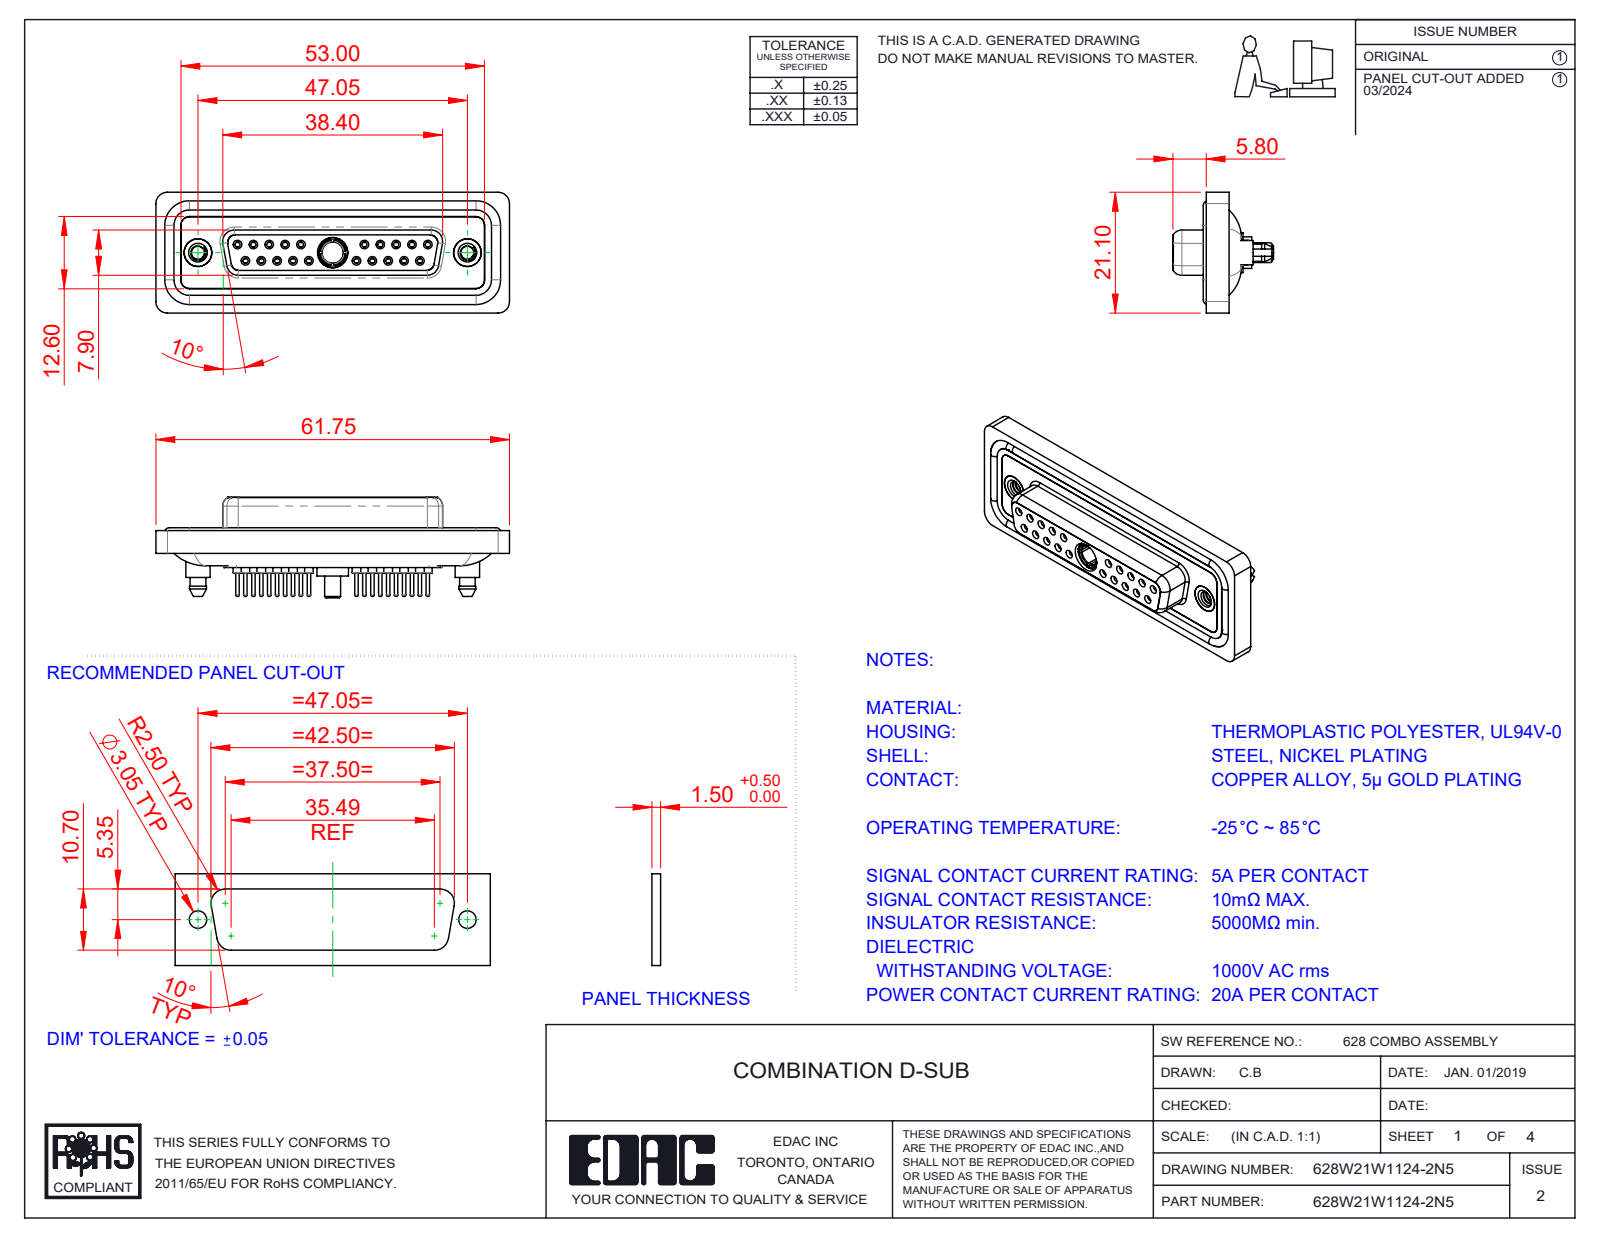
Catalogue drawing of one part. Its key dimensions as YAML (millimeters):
part_name: "628Combo Shell Front_25 Contacts; 628Combo Waterproof Housing_25 Contacts; 628Combo Contact Row 2_24; 628Combo Housing_21W1 (+5 more)"
step_written_by: "SolidWorks 2023 (CONFIG_CONTROL_DESIGN)"
units: millimeters
bodies: {solids: 29, faces: 1610, planar: 450, cylindrical: 623, other: 537}
overall_size: [61.75, 21.1, 17.55]
volume: 8508
surface_area: 14335
round_holes:
  - {diameter: 0.9, count: 20}
  - {diameter: 1.1, count: 20}
  - {diameter: 1.5, count: 20}
  - {diameter: 2, count: 20}
  - {diameter: 1.6, count: 10}
  - {diameter: 1.7, count: 10}
  - {diameter: 4.85, count: 3}
  - {diameter: 2.26, count: 2}
  - {diameter: 4, count: 2}
  - {diameter: 4.05, count: 2}
  - {diameter: 5, count: 2}
  - {diameter: 3.7, count: 1}
round_bosses_or_shafts:
  - {diameter: 2.2, count: 20}
  - {diameter: 0.6, count: 20}
  - {diameter: 1.6, count: 14}
  - {diameter: 5.4, count: 2}
  - {diameter: 4.95, count: 2}
  - {diameter: 4.8, count: 2}
  - {diameter: 4.25, count: 2}
  - {diameter: 5.5, count: 1}
partial_cylinders:
  - {radius: 1.5, count: 24}
  - {radius: 2, count: 18}
  - {radius: 1.6, count: 10}
  - {radius: 1.35, count: 8}
  - {radius: 0.25, count: 4}
  - {radius: 0.5, count: 4}
  - {radius: 0.6, count: 4}
  - {radius: 0.65, count: 4}
face_to_face_distances: [0.4, 1.8, 7.45, 6.6, 5.65, 1.6, 0.5, 7.05, 2.9, 1.1]
hole_center_spacings: [3.16, 2.77, 5.54, 5.03, 8.31, 7.48, 16.62, 19.39]
